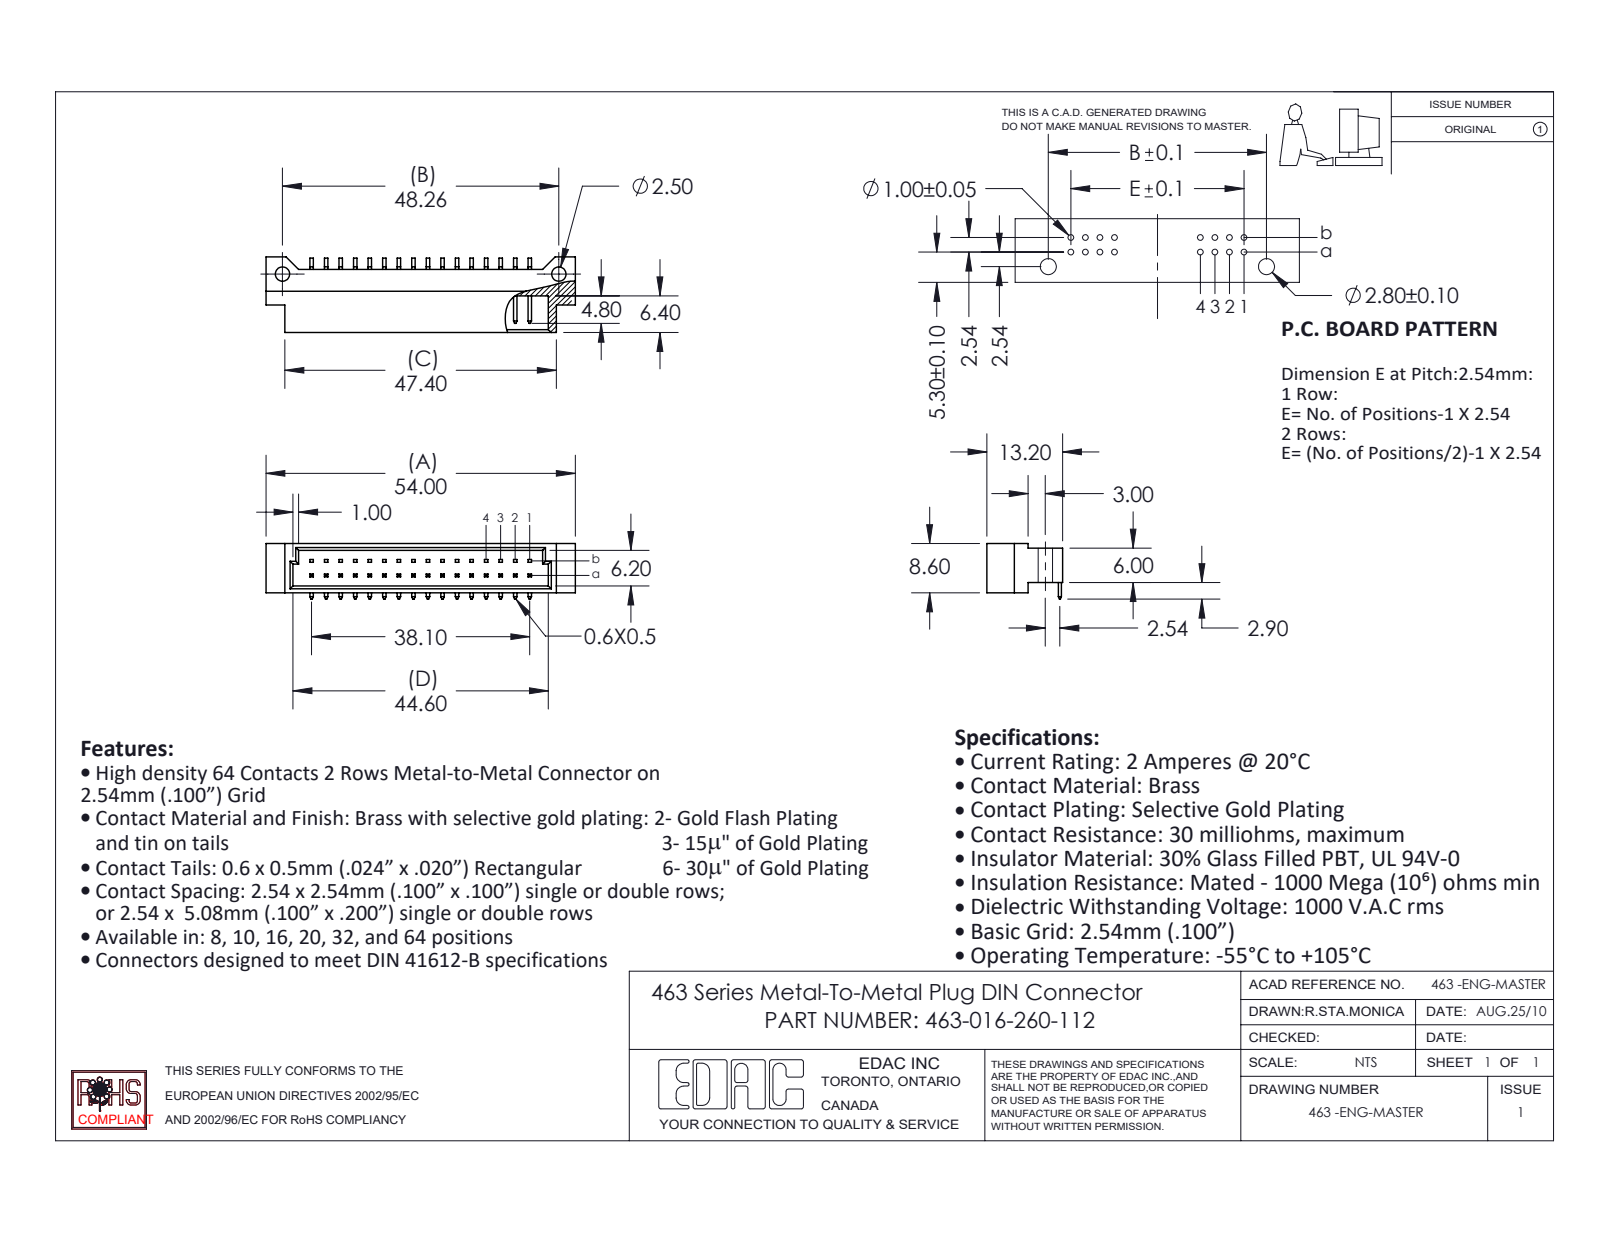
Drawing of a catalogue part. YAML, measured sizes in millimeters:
part_name: "463-016-260-112; 463 Part_32; 463-290-1"
step_written_by: "SolidWorks 2020 (CONFIG_CONTROL_DESIGN)"
units: millimeters
bodies: {solids: 17, faces: 455, planar: 419, cylindrical: 36, other: 0}
overall_size: [54, 13.2, 9.7]
volume: 2638
surface_area: 3812
round_holes:
  - {diameter: 2.5, count: 2}
partial_cylinders:
  - {radius: 1.02, count: 1}
  - {radius: 1.52, count: 1}
face_to_face_distances: [1.2, 7.4, 8.6, 0.8, 6.2, 6, 6.8, 4.6, 5.6, 7.8]
hole_center_spacings: [48.26]
